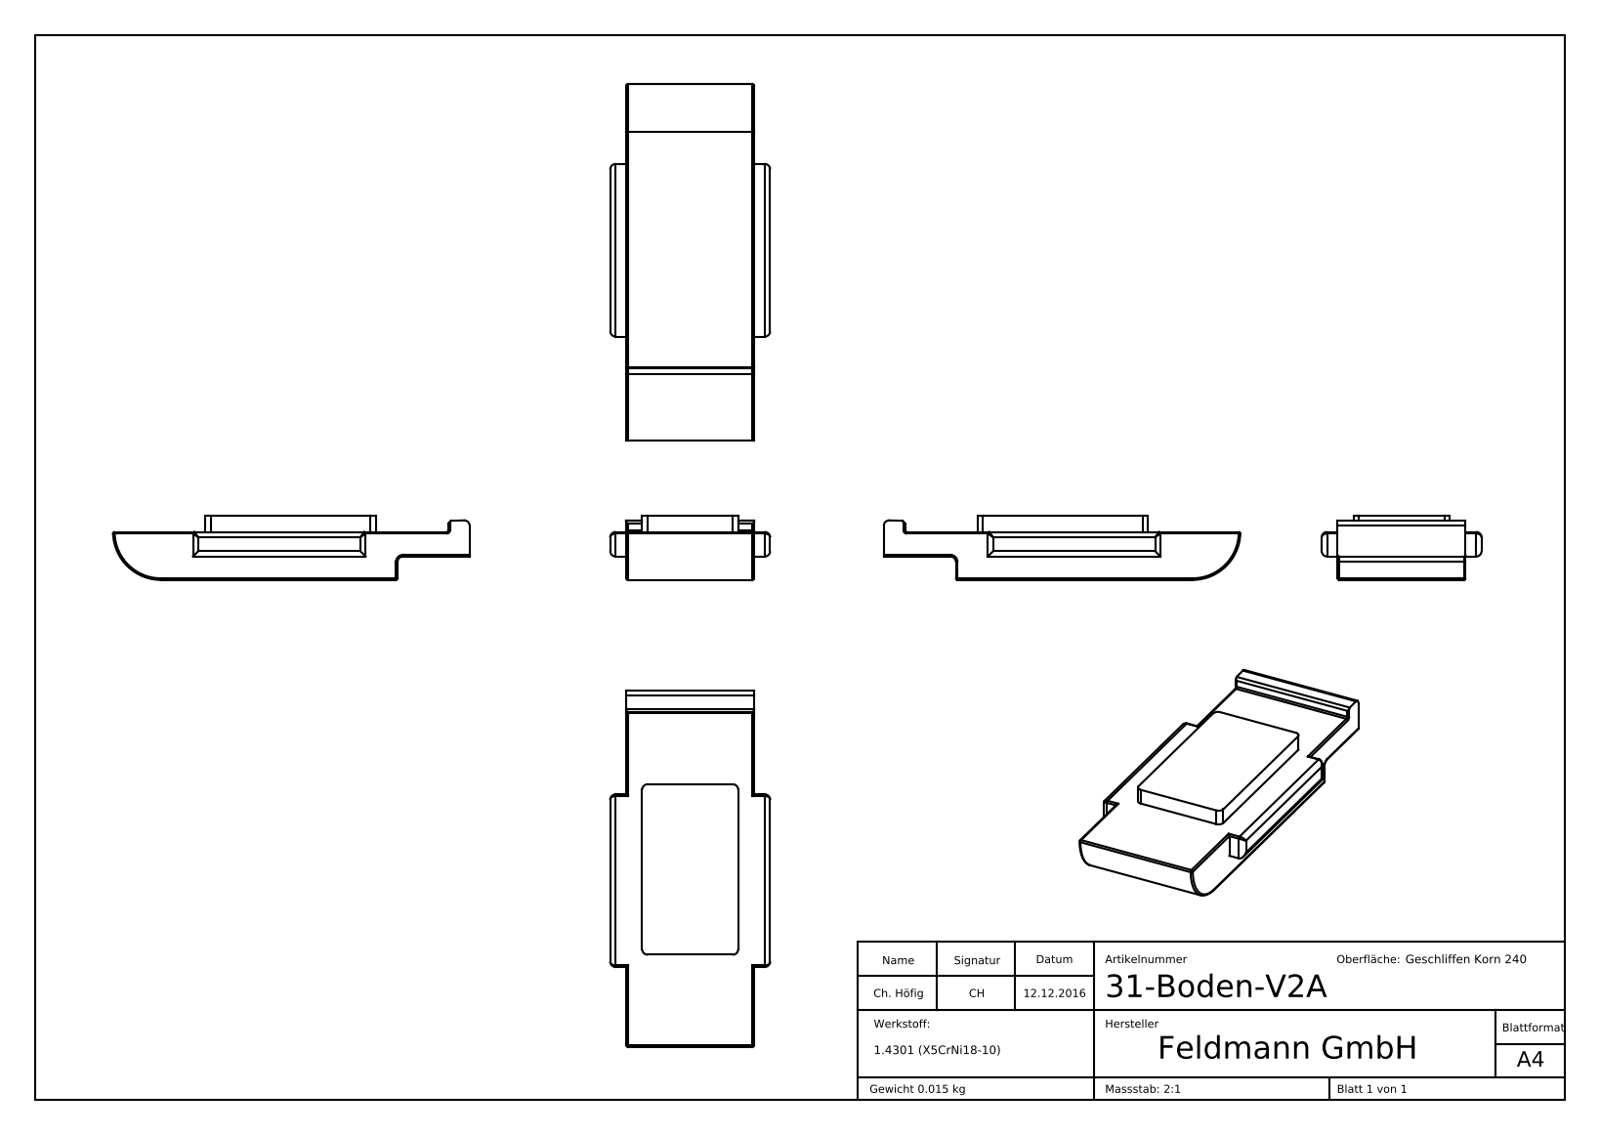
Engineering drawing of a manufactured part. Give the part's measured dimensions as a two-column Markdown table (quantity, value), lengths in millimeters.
| quantity | value |
| --- | --- |
| part name | 31-BODEN-V2A |
| STEP written by | SolidWorks 2018 (CONFIG_CONTROL_DESIGN) |
| units | millimeters |
| bodies | 1 solid, 71 faces (23 planar, 34 cylindrical, 14 other) |
| overall size | 33.46 × 15 × 6 |
| volume | 1 925 mm³ |
| surface area | 1 332 mm² |
| partial cylindrical surfaces (radius × count) | 0.15 × 15, 0.5 × 14, 4.5 × 1 |
| main face-to-face distances | 4.5, 1.5, 6, 12, 2.2, 2.3, 3.8, 10.5, 3, 13.5 |
